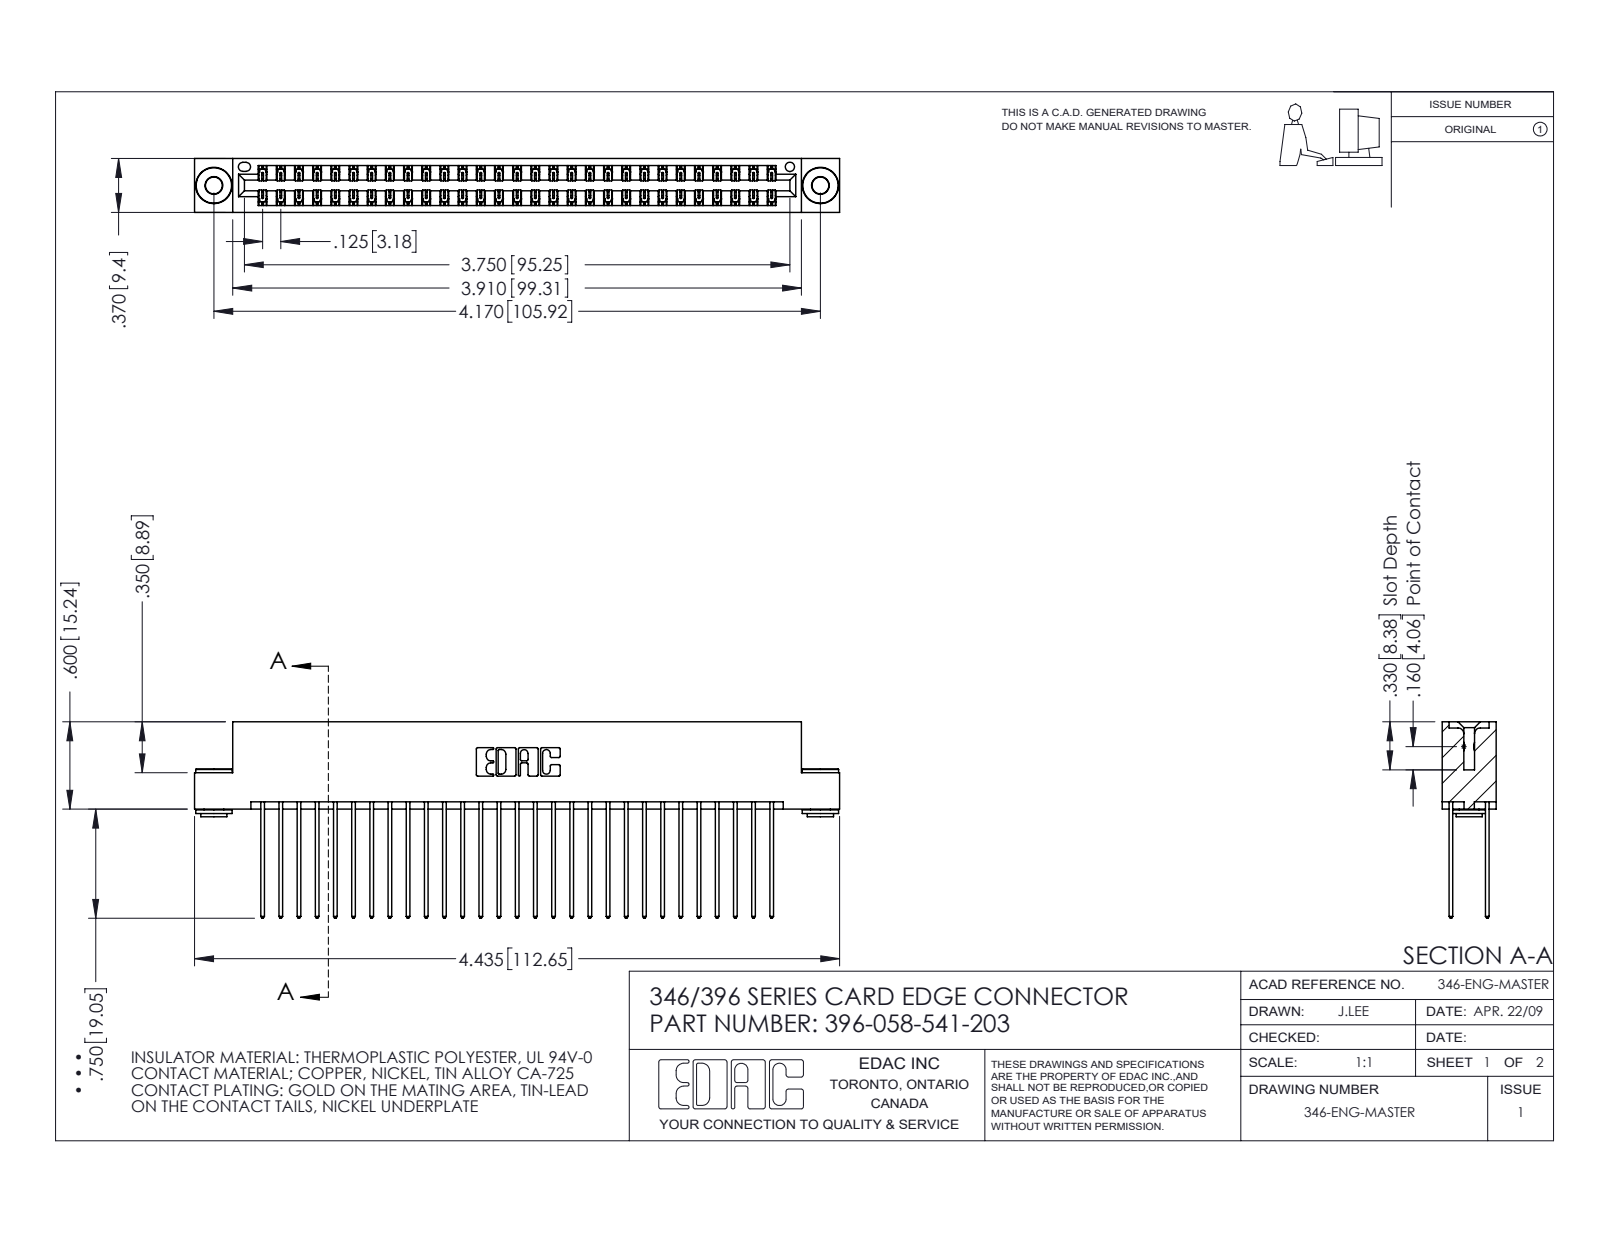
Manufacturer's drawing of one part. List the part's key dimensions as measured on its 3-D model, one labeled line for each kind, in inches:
Part name (STEP PRODUCT): 346 Part_Flush Mounting Lugs - 0.156 Dia-TH; 396-058-541-203; 345-250-002_345-250-002-102; 345-292-001_345-293-141
STEP written by: SolidWorks 2016 (CONFIG_CONTROL_DESIGN)
Units: inches
Bodies: 61 solids, 3176 faces (2116 planar, 1052 cylindrical, 8 other)
Overall size (bounding box): 4.435 × 1.35 × 0.37
Volume: 0.686 in³ · Surface area: 26.43 in²
Round holes (diameter × count): ⌀0.116 ×2, ⌀0.156 ×2, ⌀0.064 ×1
Round bosses / shafts (diameter × count): ⌀0.25 ×2, ⌀0.18 ×2, ⌀0.136 ×2
Partial cylindrical surfaces — rounded edges, fillets, slot ends (radius × count): R0.006 ×87, R0.01 ×58, R0.01 ×22, R0.007 ×6, R0.031 ×6, R0.026 ×3, R0.014 ×2, R0.022 ×2
Main face-to-face distances: 0.048, 0.322, 0.25, 0.025, 0.072, 0.298, 0.37, 0.275, 0.225, 0.148
Hole centre spacings: 0.246, 3.962, 4.17
